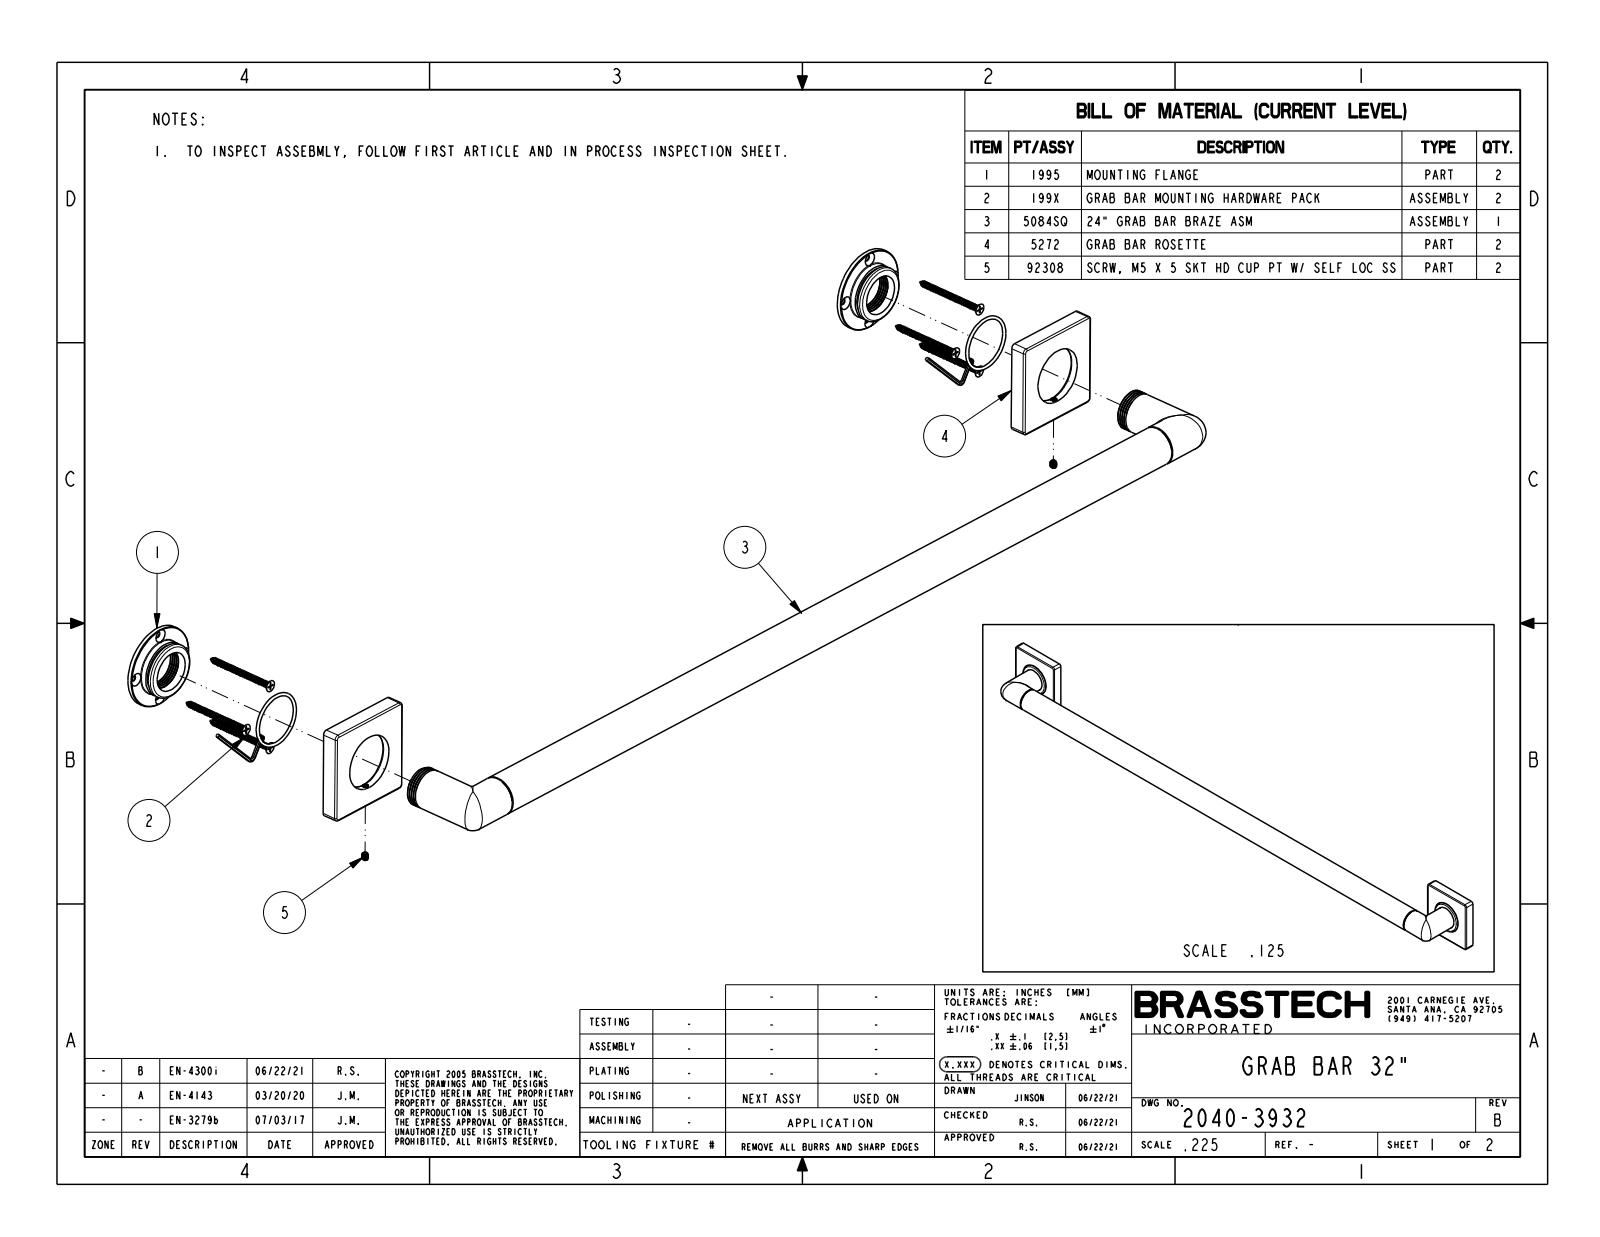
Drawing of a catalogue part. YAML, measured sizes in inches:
part_name: "2040-3932"
step_written_by: "CREO PARAMETRIC BY PTC INC, 2018400 (CONFIG_CONTROL_DESIGN)"
units: inches
bodies: {solids: 1, faces: 72, planar: 14, cylindrical: 30, other: 28}
overall_size: [35, 3, 2.755]
volume: 52.82
surface_area: 183.4
round_bosses_or_shafts:
  - {diameter: 1.25, count: 3}
  - {diameter: 1.75, count: 2}
partial_cylinders:
  - {radius: 0.125, count: 8}
  - {radius: 0.05, count: 6}
face_to_face_distances: [0.53, 3, 32, 0.6, 0.07, 35, 29]
